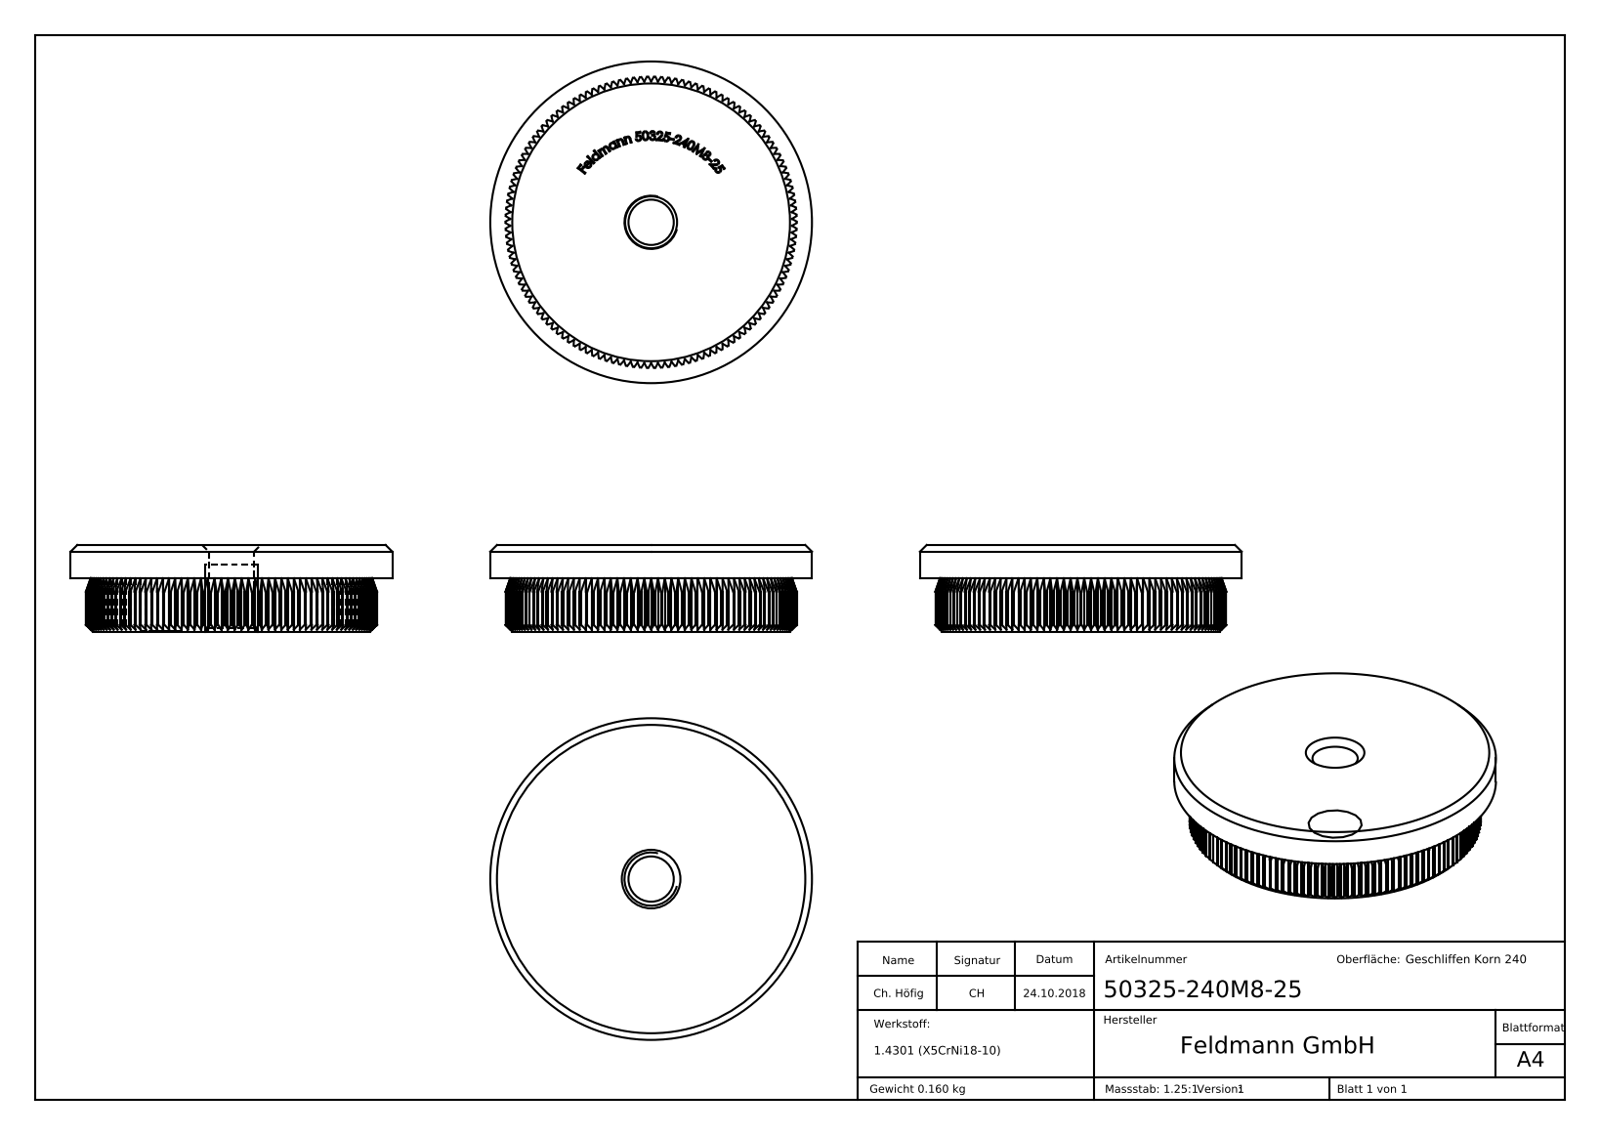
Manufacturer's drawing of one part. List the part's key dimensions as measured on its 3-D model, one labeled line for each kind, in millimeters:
Part name (STEP PRODUCT): 50325-240M8-25
STEP written by: SolidWorks 2015 (CONFIG_CONTROL_DESIGN)
Units: millimetres
Bodies: 1 solid, 821 faces (410 planar, 134 cylindrical, 277 other)
Overall size (bounding box): 48.3 × 48.3 × 13
Volume: 20 219 mm³ · Surface area: 6 299 mm²
Round holes (diameter × count): ⌀6.8 ×1
Round bosses / shafts (diameter × count): ⌀48.3 ×1
Partial cylindrical surfaces — rounded edges, fillets, slot ends (radius × count): R21.85 ×1
Main face-to-face distances: 13, 8, 5, 21.16, 21.14, 21.18, 21.12, 7.9, 12.9, 0.54
